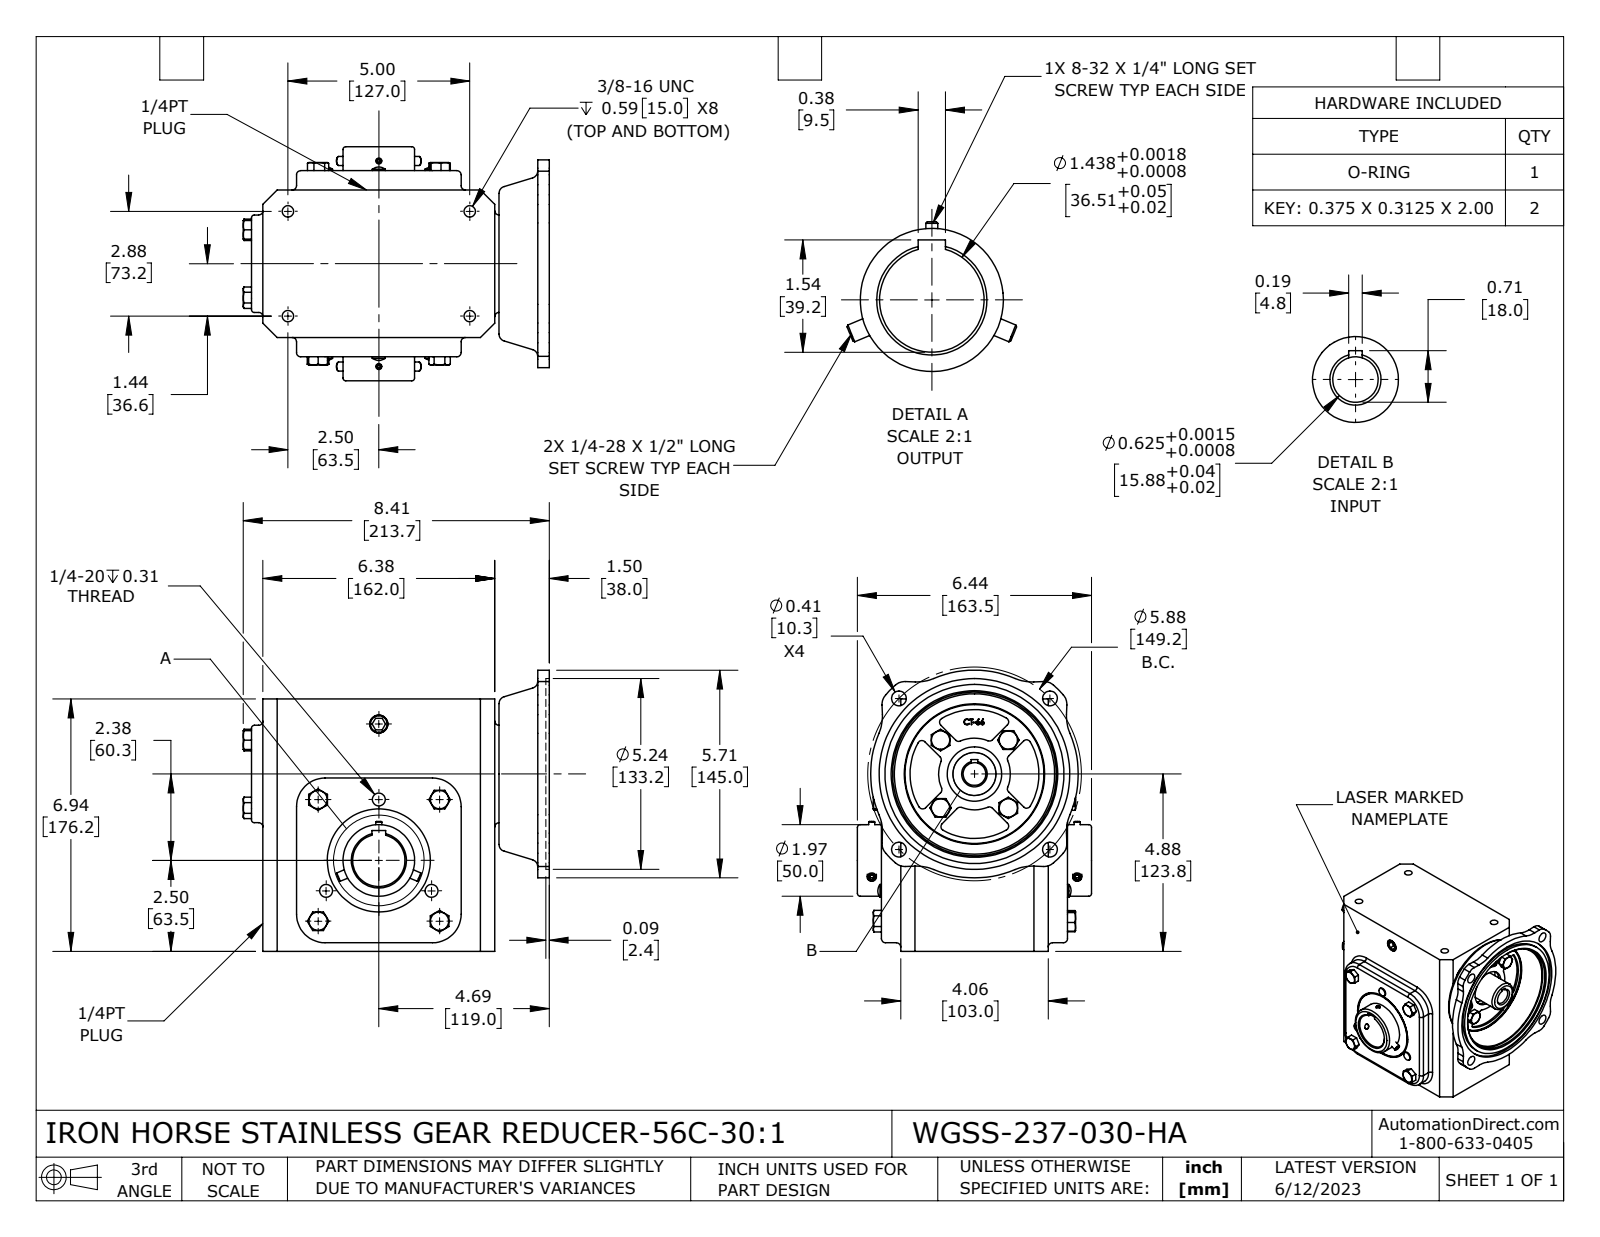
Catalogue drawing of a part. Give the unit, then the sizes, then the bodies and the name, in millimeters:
Units: millimetres
Overall size (bounding box): 213.7 × 196.3 × 163.5
Round holes (diameter × count): ⌀5.4 ×4, ⌀8 ×4, ⌀10.3 ×4, ⌀3.5 ×2, ⌀15.9 ×1, ⌀22 ×1, ⌀36.5 ×1, ⌀36.6 ×1, ⌀38 ×1, ⌀45 ×1, ⌀97 ×1, ⌀114.3 ×1
Round bosses / shafts (diameter × count): ⌀6.4 ×4, ⌀9 ×3, ⌀4.2 ×2, ⌀125 ×1, ⌀72 ×1, ⌀50 ×1, ⌀30 ×1
Partial cylindrical surfaces — rounded edges, fillets, slot ends (radius × count): R3 ×40, R10 ×12, R30 ×8, R2 ×4, R20 ×4, R25 ×1, R45 ×1, R72.5 ×1
Main face-to-face distances: 13.5, 116.5, 176.2, 8, 103, 162, 130, 200, 30, 170
Hole centre spacings: 72.6, 74.6, 125.6, 143.5, 73.2, 105.5, 105.5, 127
Volume: 3 351 000 mm³ · Surface area: 224 600 mm²
Bodies: 7 solids, 670 faces (287 planar, 195 cylindrical, 188 other)
Part name (STEP PRODUCT): WGSS-237-030-HA
STEP written by: SolidWorks 2021 (CONFIG_CONTROL_DESIGN)
